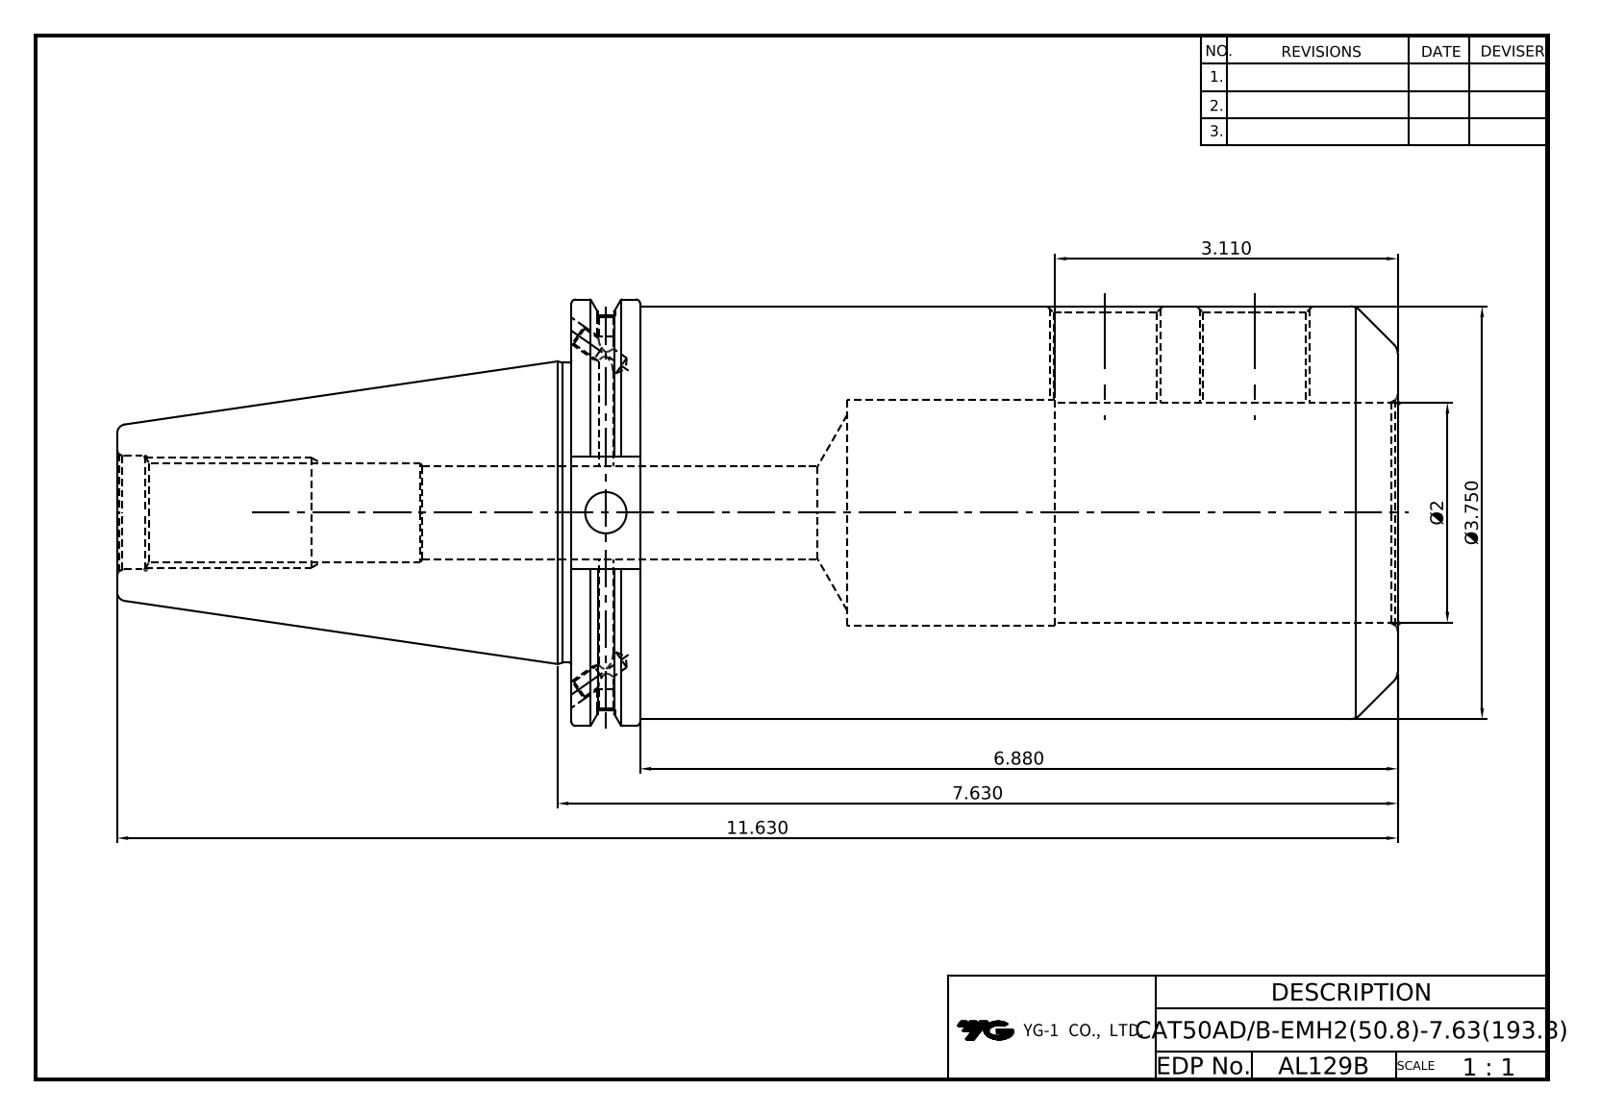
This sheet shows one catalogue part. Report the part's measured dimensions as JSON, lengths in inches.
{"part_name": "LO-CAT50ADB-EMH50.8-193.8", "step_written_by": "Autodesk Inventor 2025 (AUTOMOTIVE_DESIGN)", "units": "inches", "bodies": {"solids": 1, "faces": 87, "planar": 34, "cylindrical": 29, "other": 24}, "overall_size": [11.63, 3.875, 3.75], "volume_in3": 75.91, "surface_area_in2": 188.8, "round_holes": [[0.128, 2], [0.163, 2], [0.165, 2], [0.197, 2], [0.923, 2], [0.375, 1], [0.865, 1], [1.031, 1], [2, 1], [2.047, 1]], "round_bosses_or_shafts": [[3.875, 1], [3.75, 1], [3.594, 1], [2.726, 1]], "partial_cylinders_radius": [[0.51, 1]], "face_to_face_distances": [7.505, 2.505, 5, 2.875, 4.125, 6.63, 11.63, 1.02, 4.513, 0.389], "hole_center_spacings": [1.358]}
